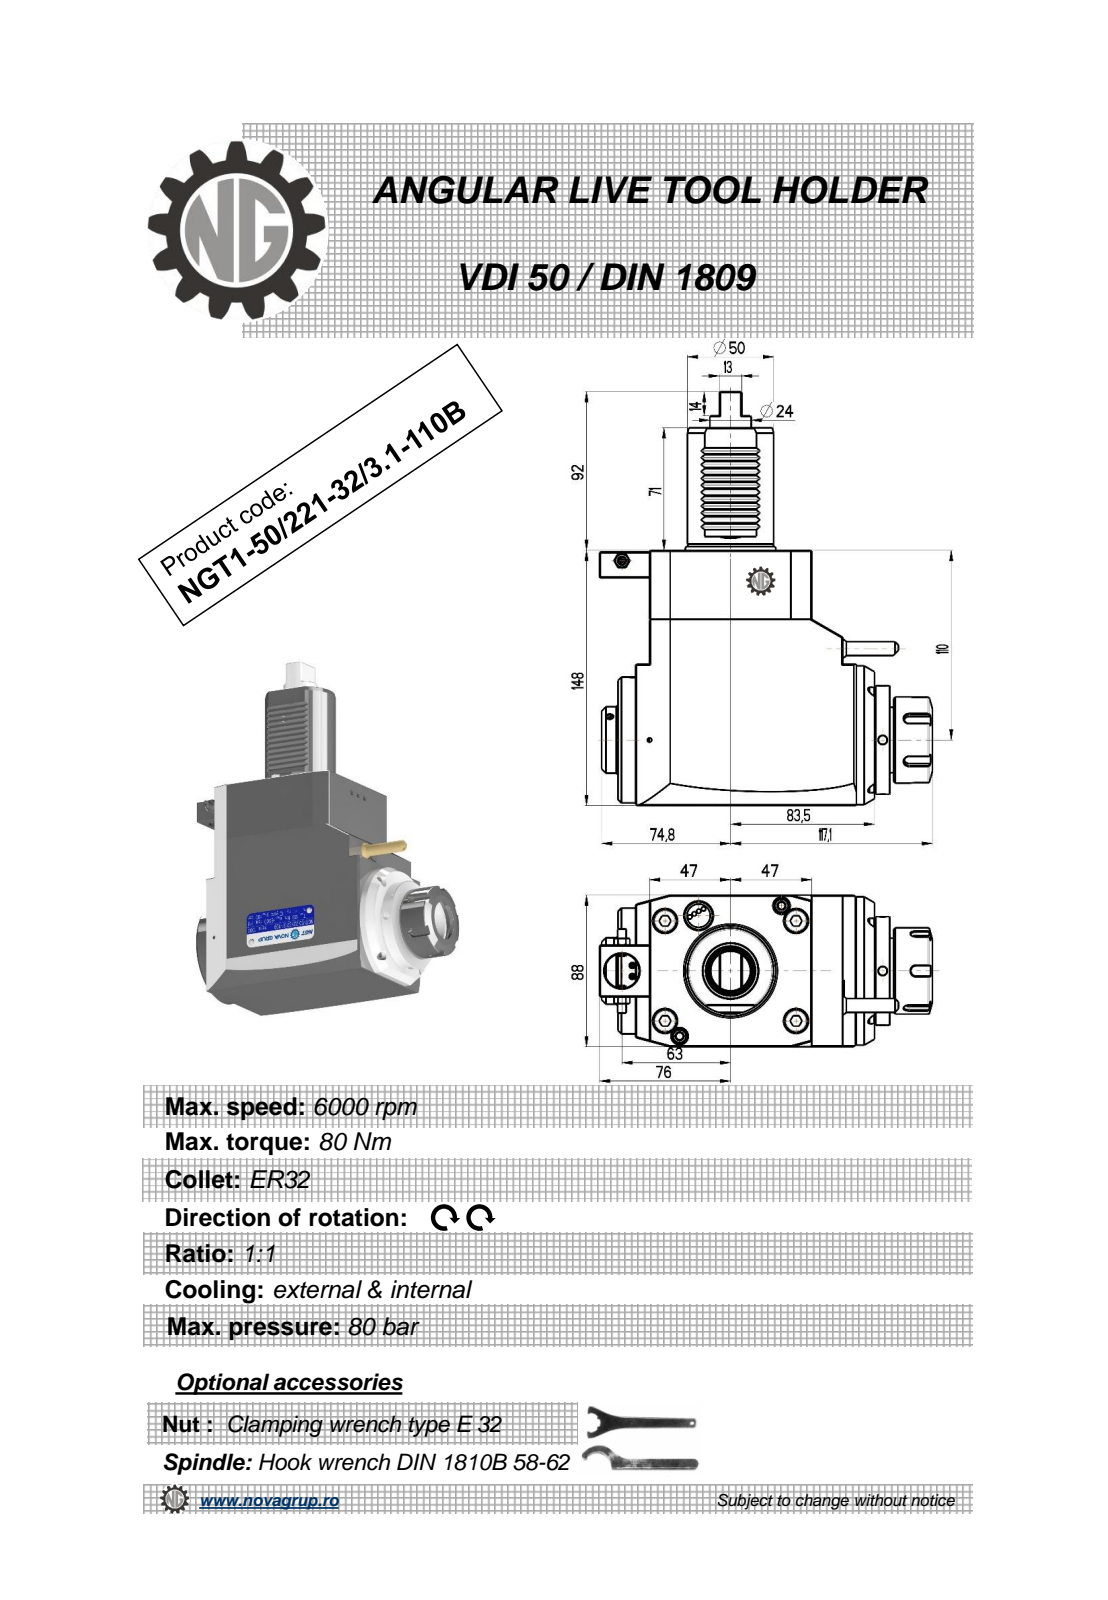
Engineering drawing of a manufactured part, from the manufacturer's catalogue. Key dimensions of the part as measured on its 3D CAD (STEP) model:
Part name (STEP PRODUCT): NGT1_50_221_32_3_1_110B
STEP written by: PRO/ENGINEER BY PARAMETRIC TECHNOLOGY CORPORATION, 2010280 (CONFIG_CONTROL_DESIGN)
Units: millimetres
Bodies: 1 solid, 423 faces (198 planar, 98 cylindrical, 127 other)
Overall size (bounding box): 240 × 193.1 × 88
Volume: 1 814 000 mm³ · Surface area: 112 671 mm²
Round holes (diameter × count): ⌀5 ×3, ⌀3.8 ×2, ⌀4 ×2, ⌀3 ×1, ⌀9.5 ×1, ⌀20 ×1, ⌀27 ×1
Round bosses / shafts (diameter × count): ⌀50 ×2, ⌀86 ×1, ⌀73 ×1, ⌀63 ×1, ⌀50.5 ×1, ⌀41 ×1, ⌀40 ×1, ⌀38.5 ×1
Partial cylindrical surfaces — rounded edges, fillets, slot ends (radius × count): R0.26 ×12, R0.3 ×12, R0.2 ×6, R3 ×5, R0.8 ×2
Main face-to-face distances: 88, 148, 8, 94, 18.3, 130.5, 36.5, 120, 112.3, 148.8
Hole centre spacings: 9, 101.9, 18, 49.73, 52.46, 56.51, 56.65, 101.5
